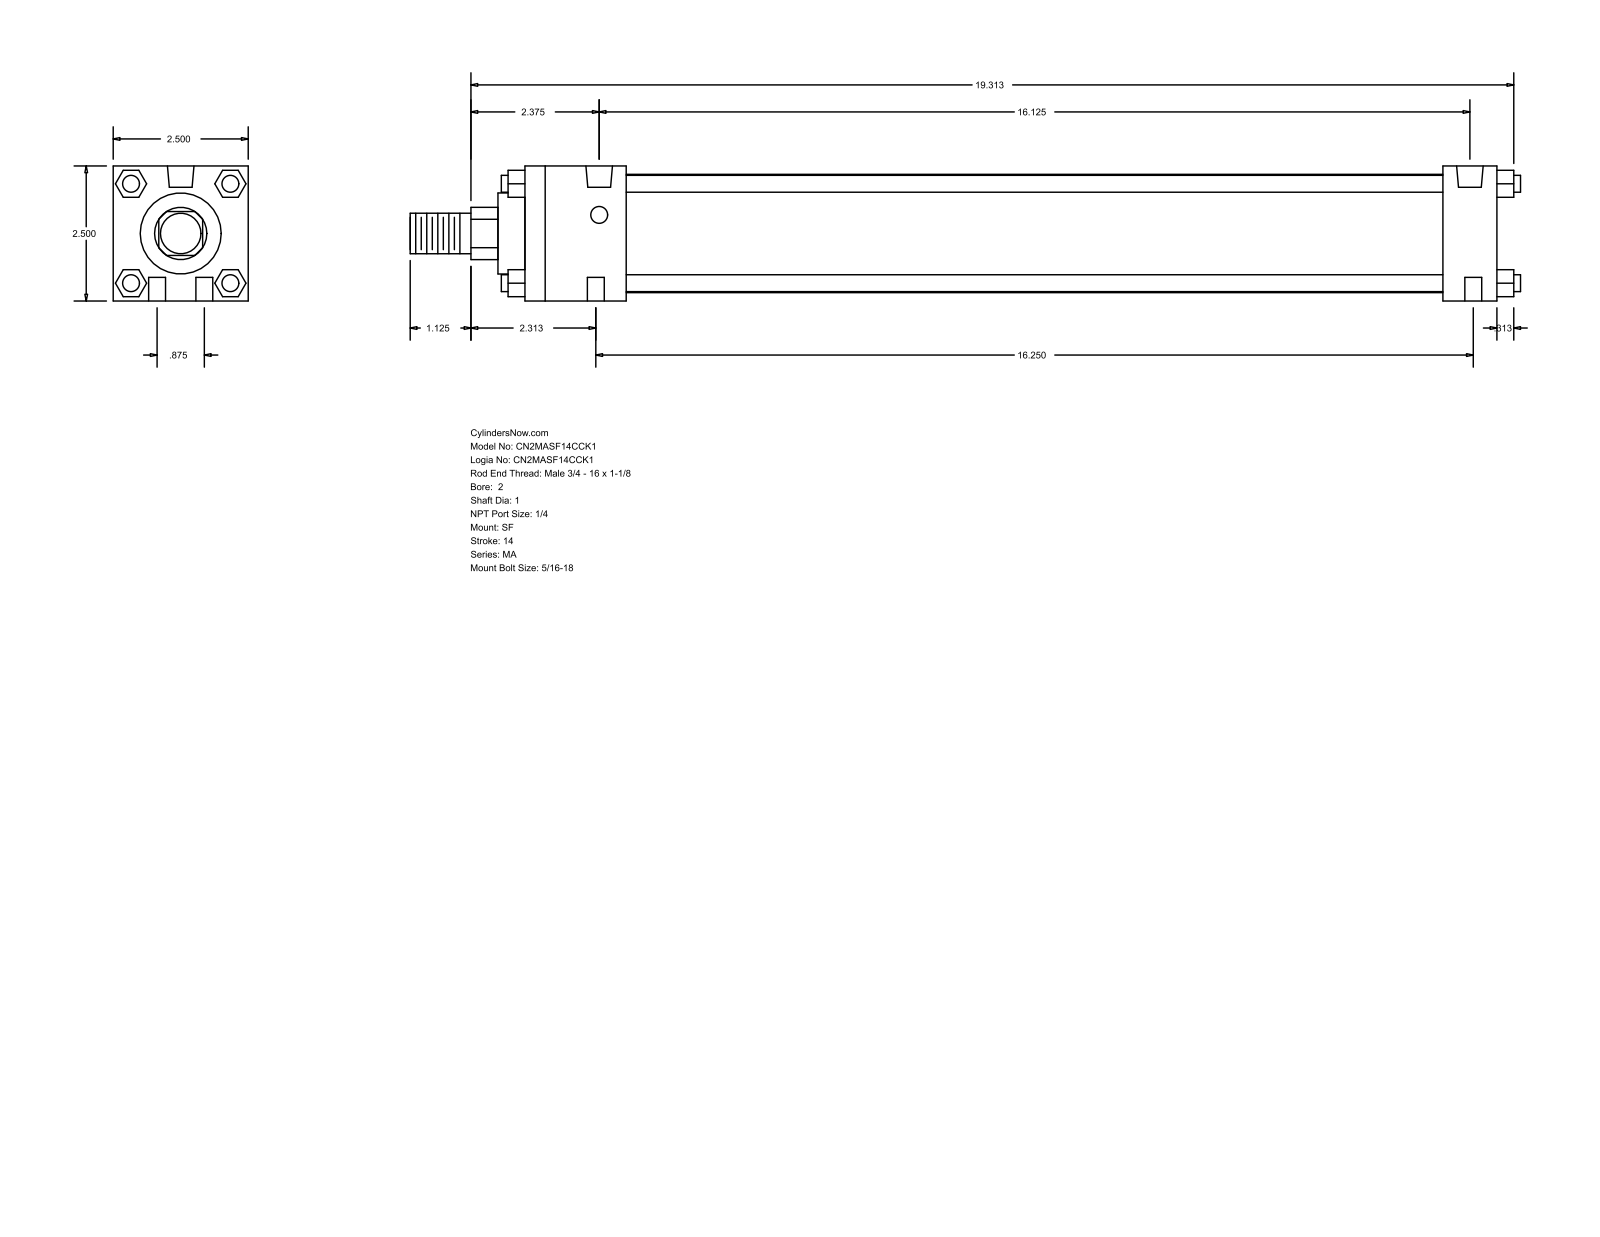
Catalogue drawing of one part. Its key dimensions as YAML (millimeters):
part_name: "MA_SF__0200_1"
step_written_by: "GSSL Pune (CONFIG_CONTROL_DESIGN)"
units: millimeters
bodies: {solids: 0, faces: 124, planar: 94, cylindrical: 30, other: 0}
overall_size: [522.29, 63.5, 63.5]
round_holes:
  - {diameter: 7.94, count: 6}
  - {diameter: 12.49, count: 2}
round_bosses_or_shafts:
  - {diameter: 7.94, count: 4}
  - {diameter: 55.63, count: 1}
  - {diameter: 38.1, count: 1}
  - {diameter: 25.4, count: 1}
  - {diameter: 19.05, count: 1}
partial_cylinders:
  - {radius: 12.29, count: 1}
face_to_face_distances: [63.5, 457.2, 12.7, 25.4, 431.8, 47.63, 384.17, 409.57, 40.47, 23.37]
hole_center_spacings: [11.22, 411.31, 22.22, 409.57, 412.75, 413.35]
